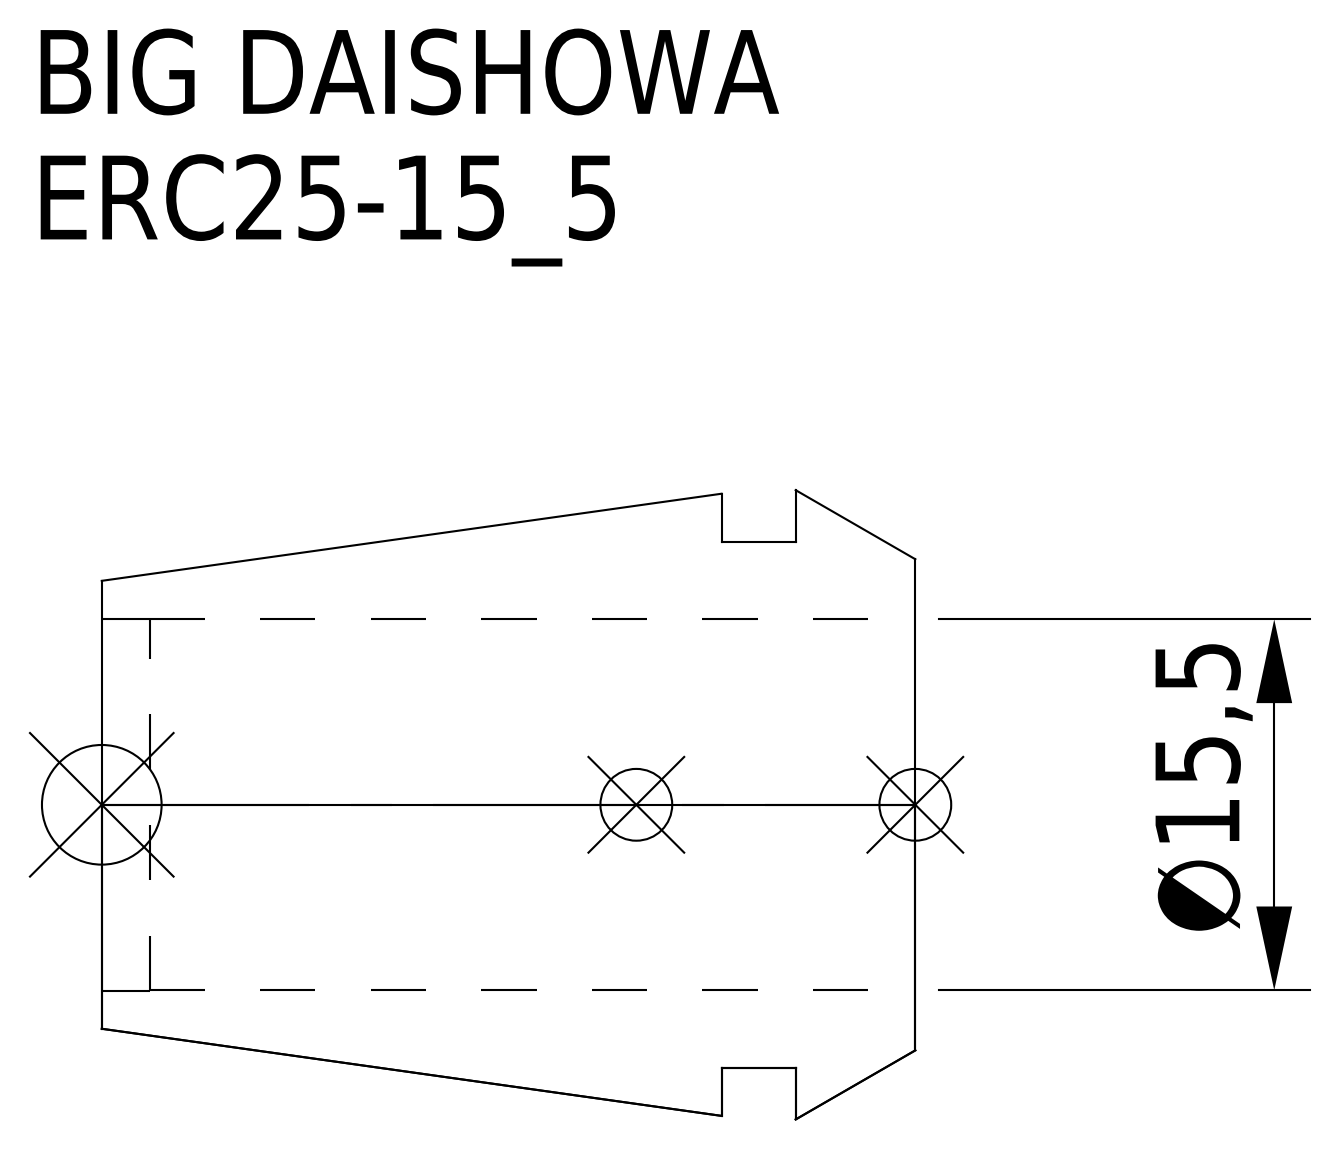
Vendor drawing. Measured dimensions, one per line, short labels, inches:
name: ERC25-15_5
written by: CREO PARAMETRIC BY PTC INC, 2016380 (AUTOMOTIVE_DESIGN)
unit: in
bodies: 1 solid, 15 faces (5 planar, 6 cylindrical, 4 other)
size: 1.339 × 1.035 × 1.035
volume: 0.438 in³; area: 7.246 in²
holes: 1× ⌀0.61, 1× ⌀0.612
bosses: 1× ⌀0.866
face distances: 0.122, 0.197, 0.319, 1.339, 1.142, 1.02, 1.26, 1.063, 0.941, 0.079
